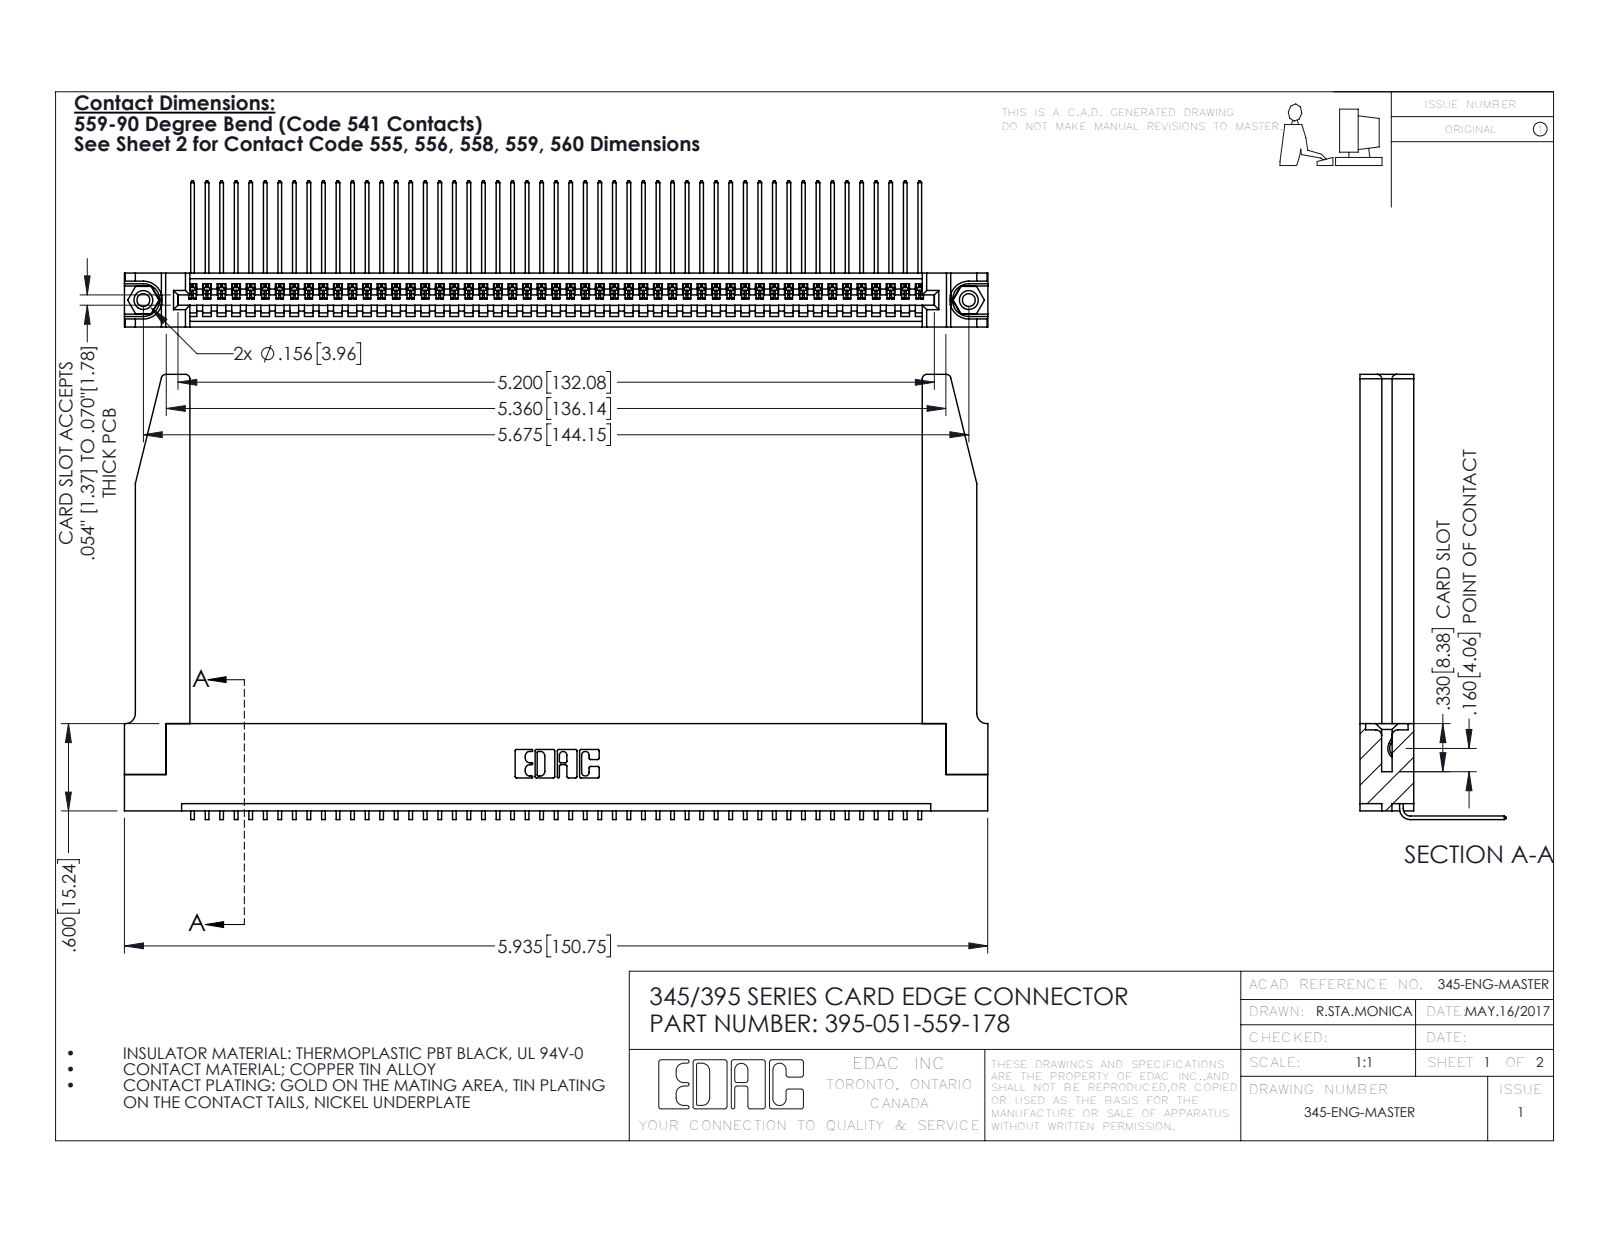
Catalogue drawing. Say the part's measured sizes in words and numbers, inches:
The part is named "345-220-078_345-220-078; 345-250-001_345-250-001-102; 345 Part_Flush Mounting Lugs - 0.156 Dia-TH; 345-292-001_558 559 Tail - 1 (+1 more)". Its 3-D file was written by "SolidWorks 2016 (CONFIG_CONTROL_DESIGN)". It is 56 solids with 3420 faces: 2364 planar, 1004 cylindrical and 52 other. Overall it measures 5.936 by 3.059 by 1.005 inches. Its volume is 1.363 cubic inches and its surface area 42.35 square inches. Round holes: 2 of diameter 0.089, 2 of diameter 0.125, 2 of diameter 0.156, 1 of diameter 0.064. Round bosses or shafts: 2 of diameter 0.155. Partial cylindrical surfaces (rounded edges, fillets, slot ends): 102 of radius 0.006, 22 of radius 0.01, 8 of radius 0.03, 6 of radius 0.007, 6 of radius 0.031, 3 of radius 0.026, 2 of radius 0.031, 2 of radius 0.04. The main face-to-face distances are 0.37, 0.072, 0.298, 0.2, 0.098, 0.272, 0.025, 0.225, 0.148, 0.15. The hole center spacings are 0.27, 5.439, 5.675.
